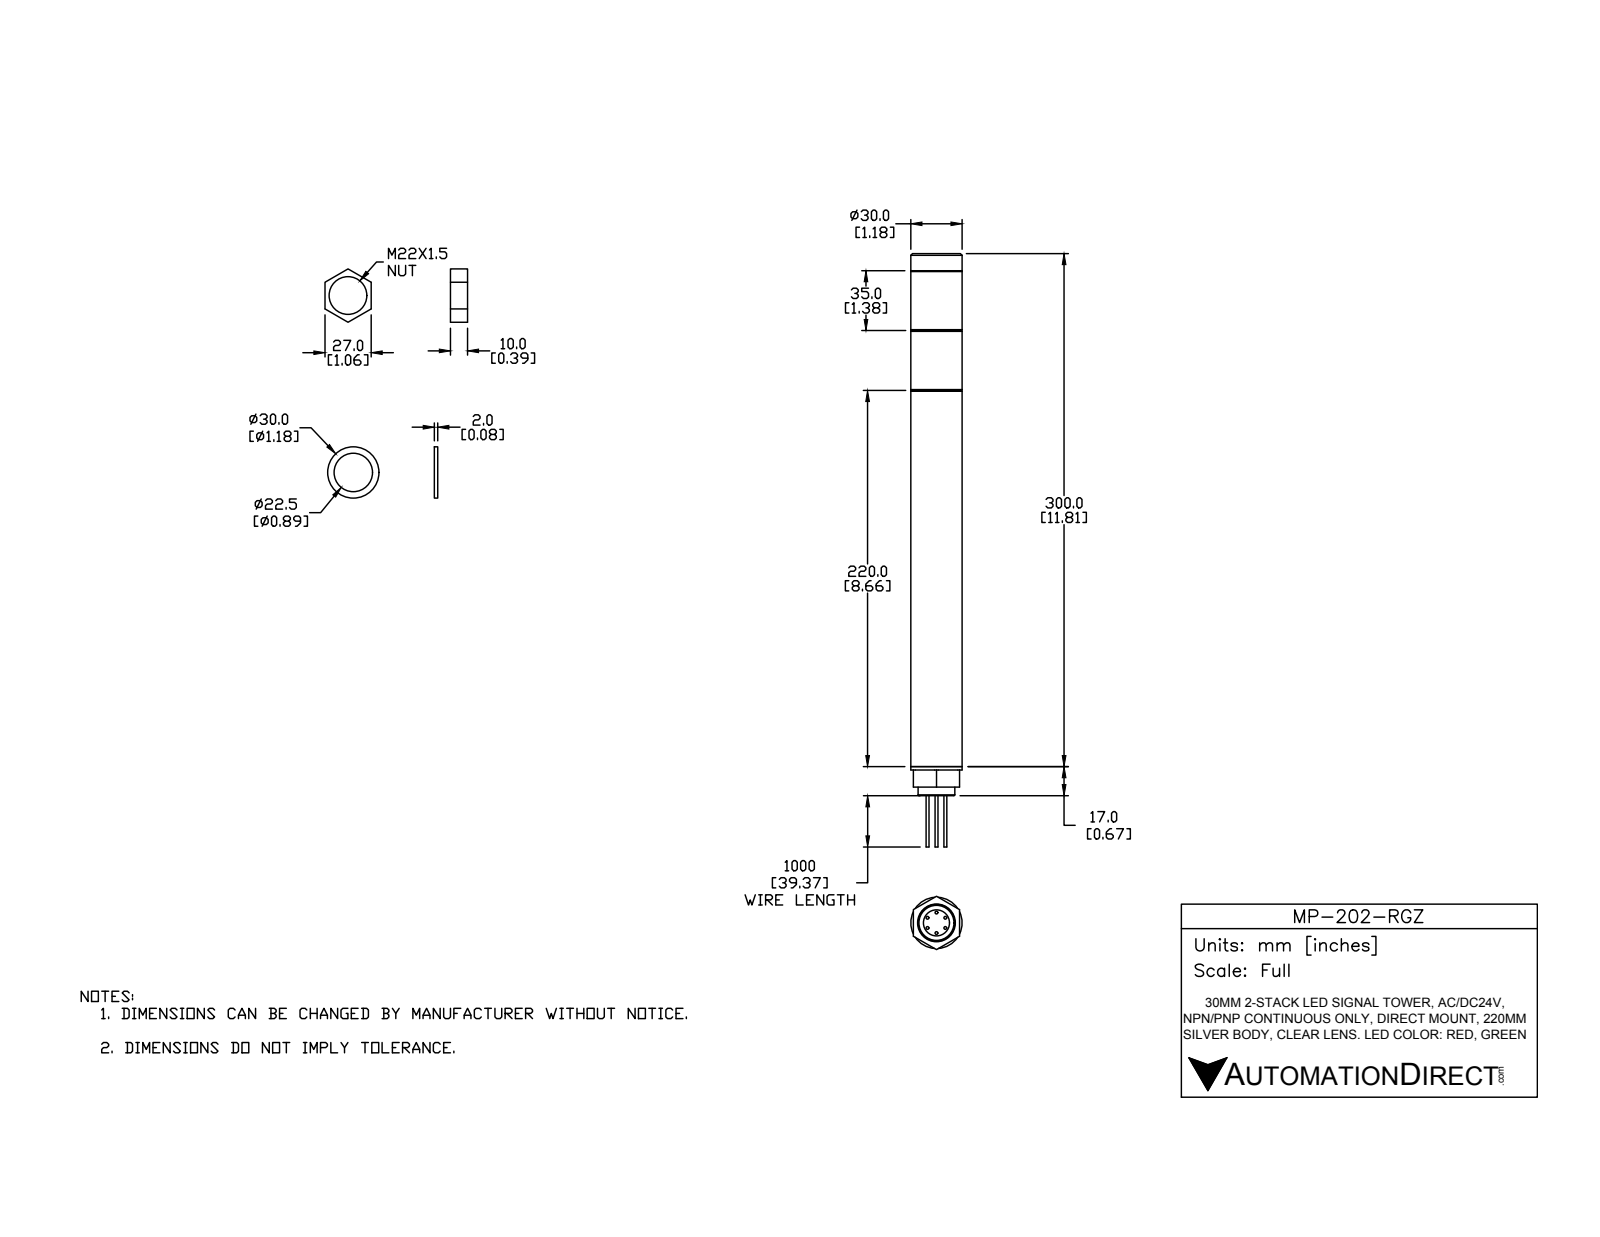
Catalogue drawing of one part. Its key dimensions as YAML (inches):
part_name: "MP-202-RGZ"
step_written_by: "SolidWorks 2016 (AUTOMOTIVE_DESIGN)"
units: inches
bodies: {solids: 13, faces: 103, planar: 49, cylindrical: 38, other: 16}
overall_size: [13.661, 1.228, 1.181]
volume: 12.69
surface_area: 68.29
round_holes:
  - {diameter: 0.126, count: 1}
  - {diameter: 0.303, count: 1}
  - {diameter: 0.602, count: 1}
  - {diameter: 0.815, count: 1}
  - {diameter: 0.866, count: 1}
round_bosses_or_shafts:
  - {diameter: 0.067, count: 6}
  - {diameter: 1.181, count: 1}
  - {diameter: 0.846, count: 1}
  - {diameter: 0.197, count: 1}
face_to_face_distances: [1.378, 2.756, 8.74, 10.118, 1.772, 11.89, 8.661, 10.039, 11.417, 0.394]
